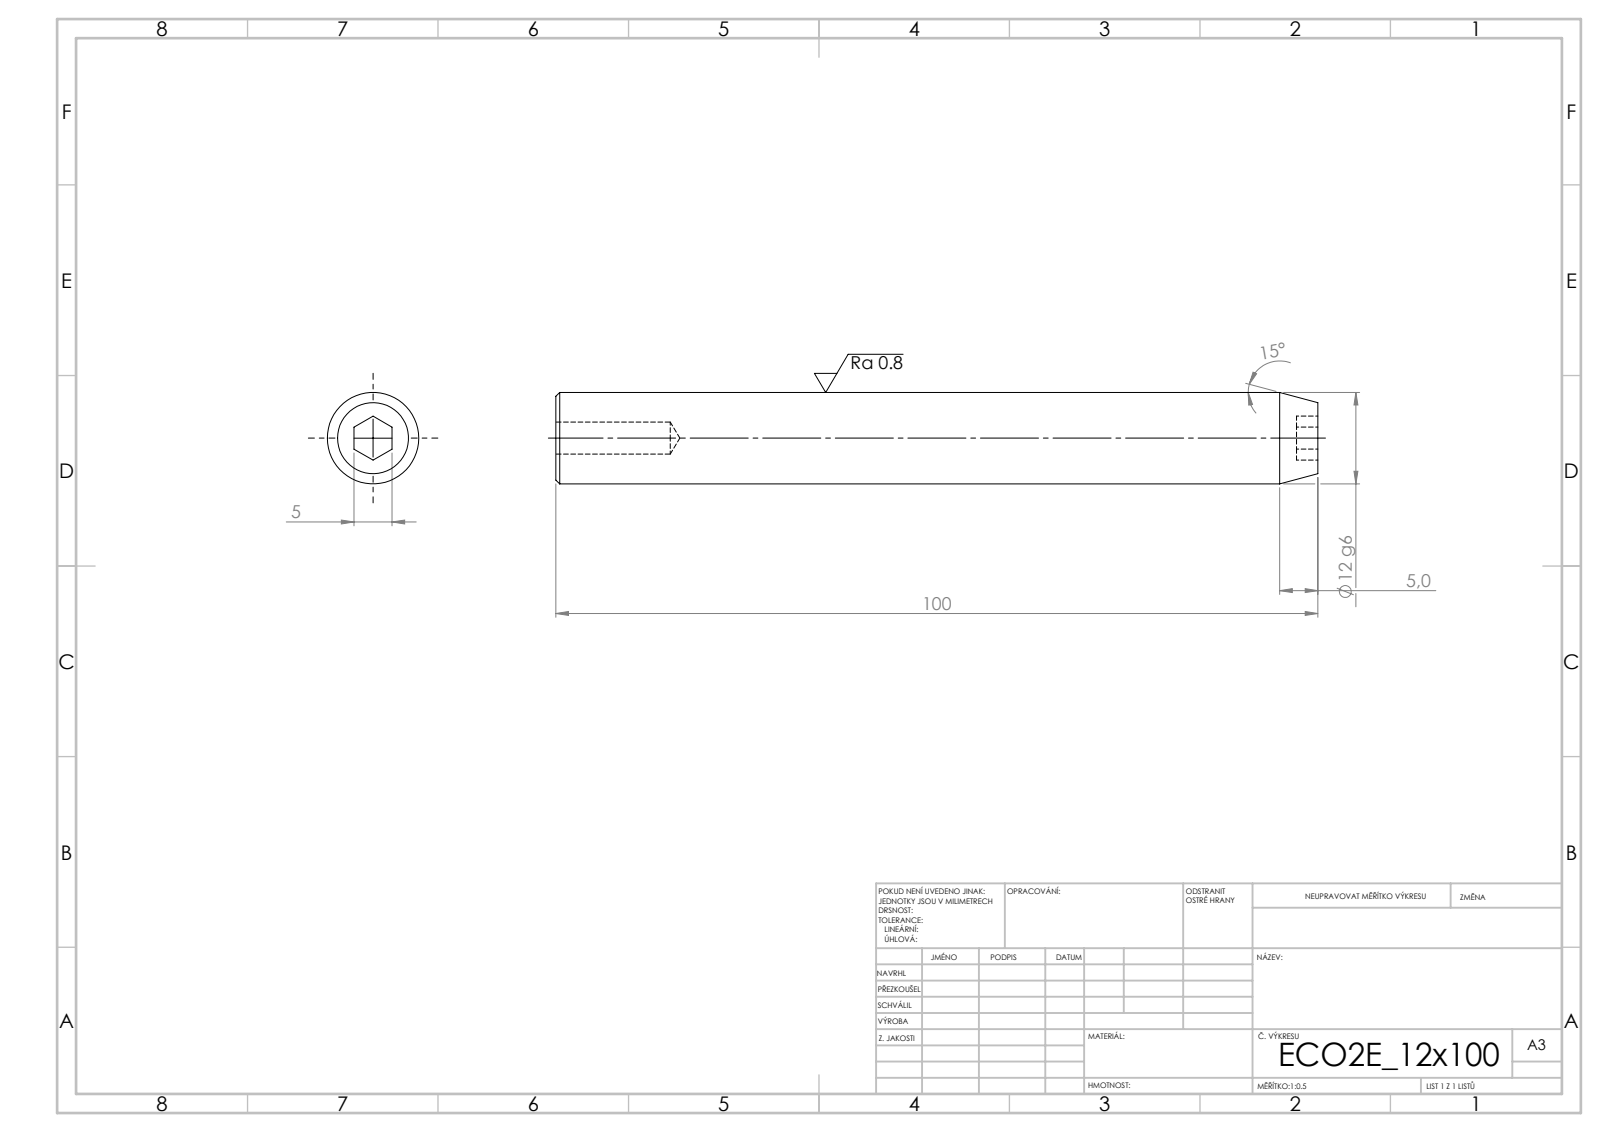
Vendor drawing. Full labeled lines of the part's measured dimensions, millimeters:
STEP written by: SolidWorks 2019 (CONFIG_CONTROL_DESIGN)
Units: millimetres
Bodies: 1 solid, 19 faces (9 planar, 4 cylindrical, 6 other)
Overall size (bounding box): 100 × 12 × 12
Volume: 10 914 mm³ · Surface area: 4 173 mm²
Round holes (diameter × count): ⌀4.2 ×1
Round bosses / shafts (diameter × count): ⌀12 ×1
Main face-to-face distances: 100, 5, 2.8, 97.2
